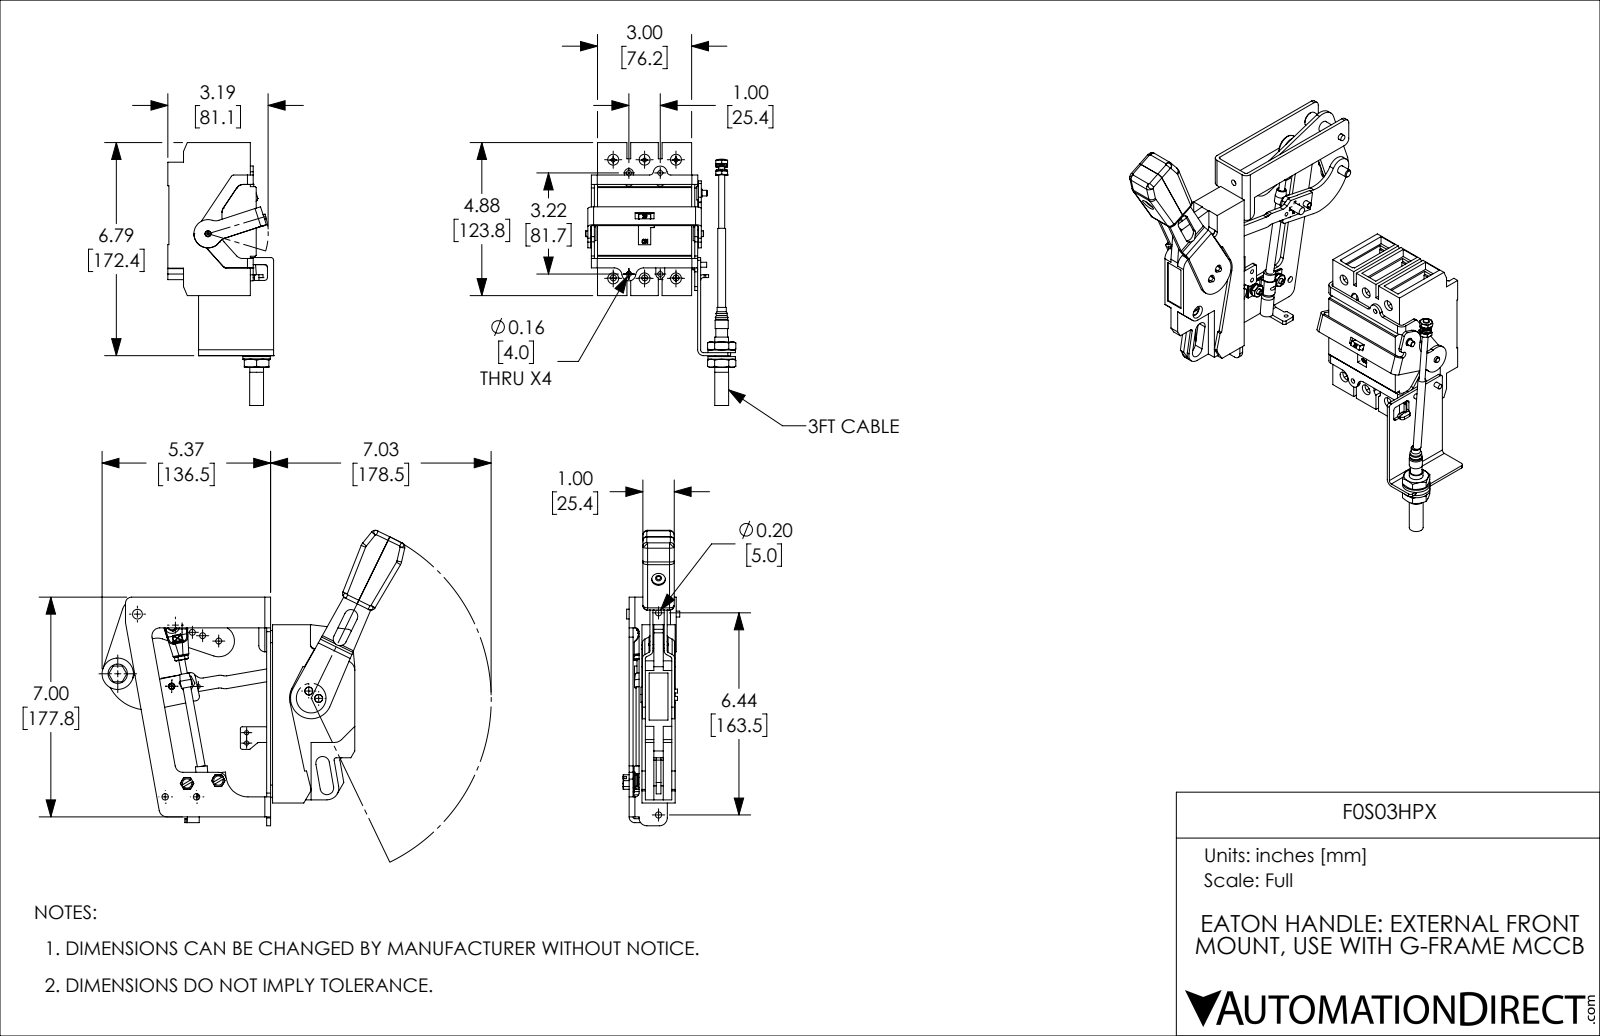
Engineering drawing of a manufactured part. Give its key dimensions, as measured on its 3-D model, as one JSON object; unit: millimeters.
{"part_name": "F0S03HPX_BREAKER; F0S03HPX_HANDLE; F0S03HPX", "step_written_by": "SolidWorks 2019 (CONFIG_CONTROL_DESIGN)", "units": "millimeters", "bodies": {"solids": 77, "faces": 2152, "planar": 1122, "cylindrical": 779, "other": 251}, "overall_size": [297.4, 255.7, 245.1], "volume_mm3": 838000, "surface_area_mm2": 282300, "round_holes": [[4, 8], [4.8, 8], [5.2, 6], [8.8, 6], [4.8, 5], [3.2, 3], [3.2, 3], [4.9, 3], [5, 3], [6.4, 3], [6.4, 3], [3.5, 2]], "round_bosses_or_shafts": [[6.4, 9], [9.5, 5], [11.2, 4], [9.5, 3], [8.7, 3], [7.9, 3], [6.2, 3], [4.6, 3]], "partial_cylinders_radius": [[6.4, 31], [2.3, 23], [1.6, 17], [3.2, 17], [0.5, 12], [3.8, 12], [0.8, 11], [0.8, 10]], "face_to_face_distances": [2.4, 3.2, 15.1, 135.7, 211.9, 76.2, 138.9, 215.1, 4.7, 2.8], "hole_center_spacings": [25.4, 50.8, 0.4, 16.4, 86.3, 93, 99.1, 141.5]}
